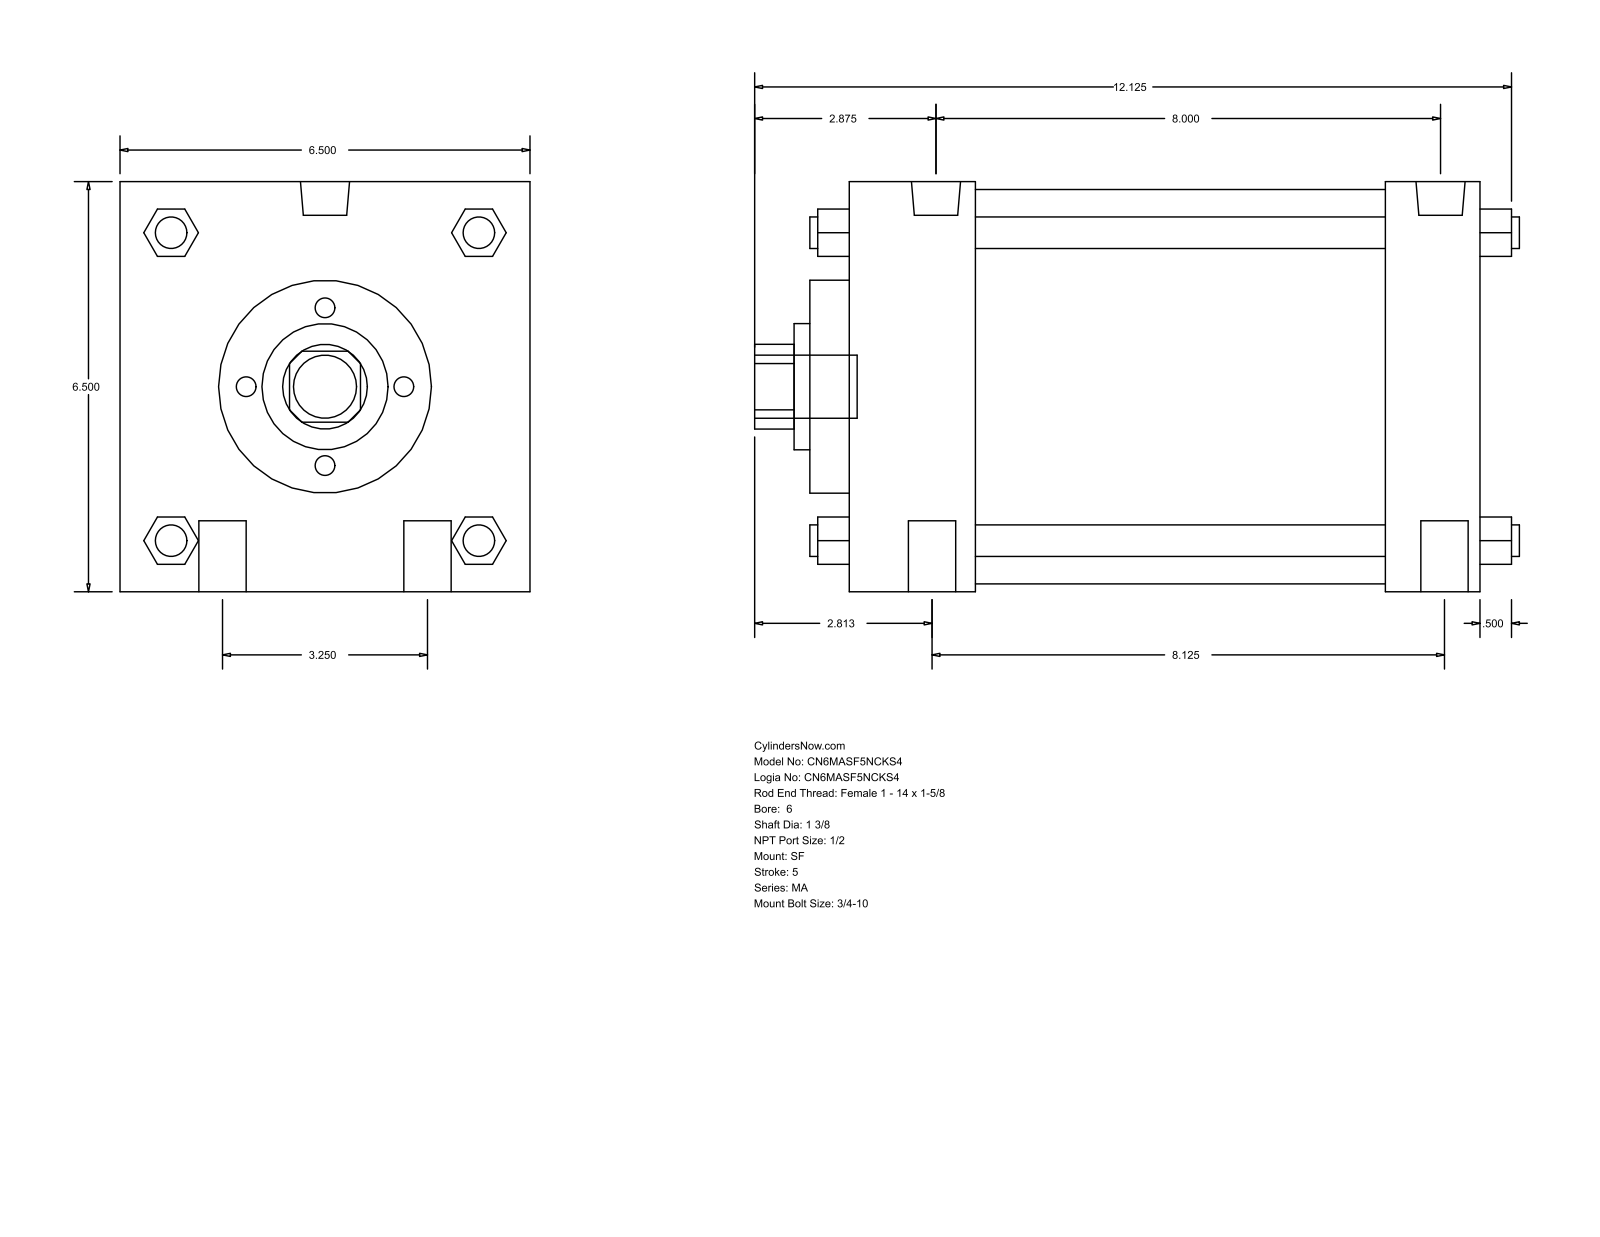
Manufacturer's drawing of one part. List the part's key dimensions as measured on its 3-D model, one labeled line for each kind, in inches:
Part name (STEP PRODUCT): MA_SF__0600_1.375
STEP written by: GSSL Pune (CONFIG_CONTROL_DESIGN)
Units: inches
Bodies: 0 solids, 126 faces (95 planar, 31 cylindrical, 0 other)
Overall size (bounding box): 12.125 × 6.5 × 6.5
Round holes (diameter × count): ⌀1.375 ×1, ⌀2 ×1, ⌀3.375 ×1, ⌀6.25 ×1
Round bosses / shafts (diameter × count): ⌀0.75 ×4, ⌀0.5 ×4, ⌀0.778 ×2, ⌀0.687 ×2, ⌀1 ×1
Partial cylindrical surfaces — rounded edges, fillets, slot ends (radius × count): R0.672 ×1
Main face-to-face distances: 6.5, 10, 8.5, 2, 1.5, 8, 0.625, 2.625, 9.125, 10.625
